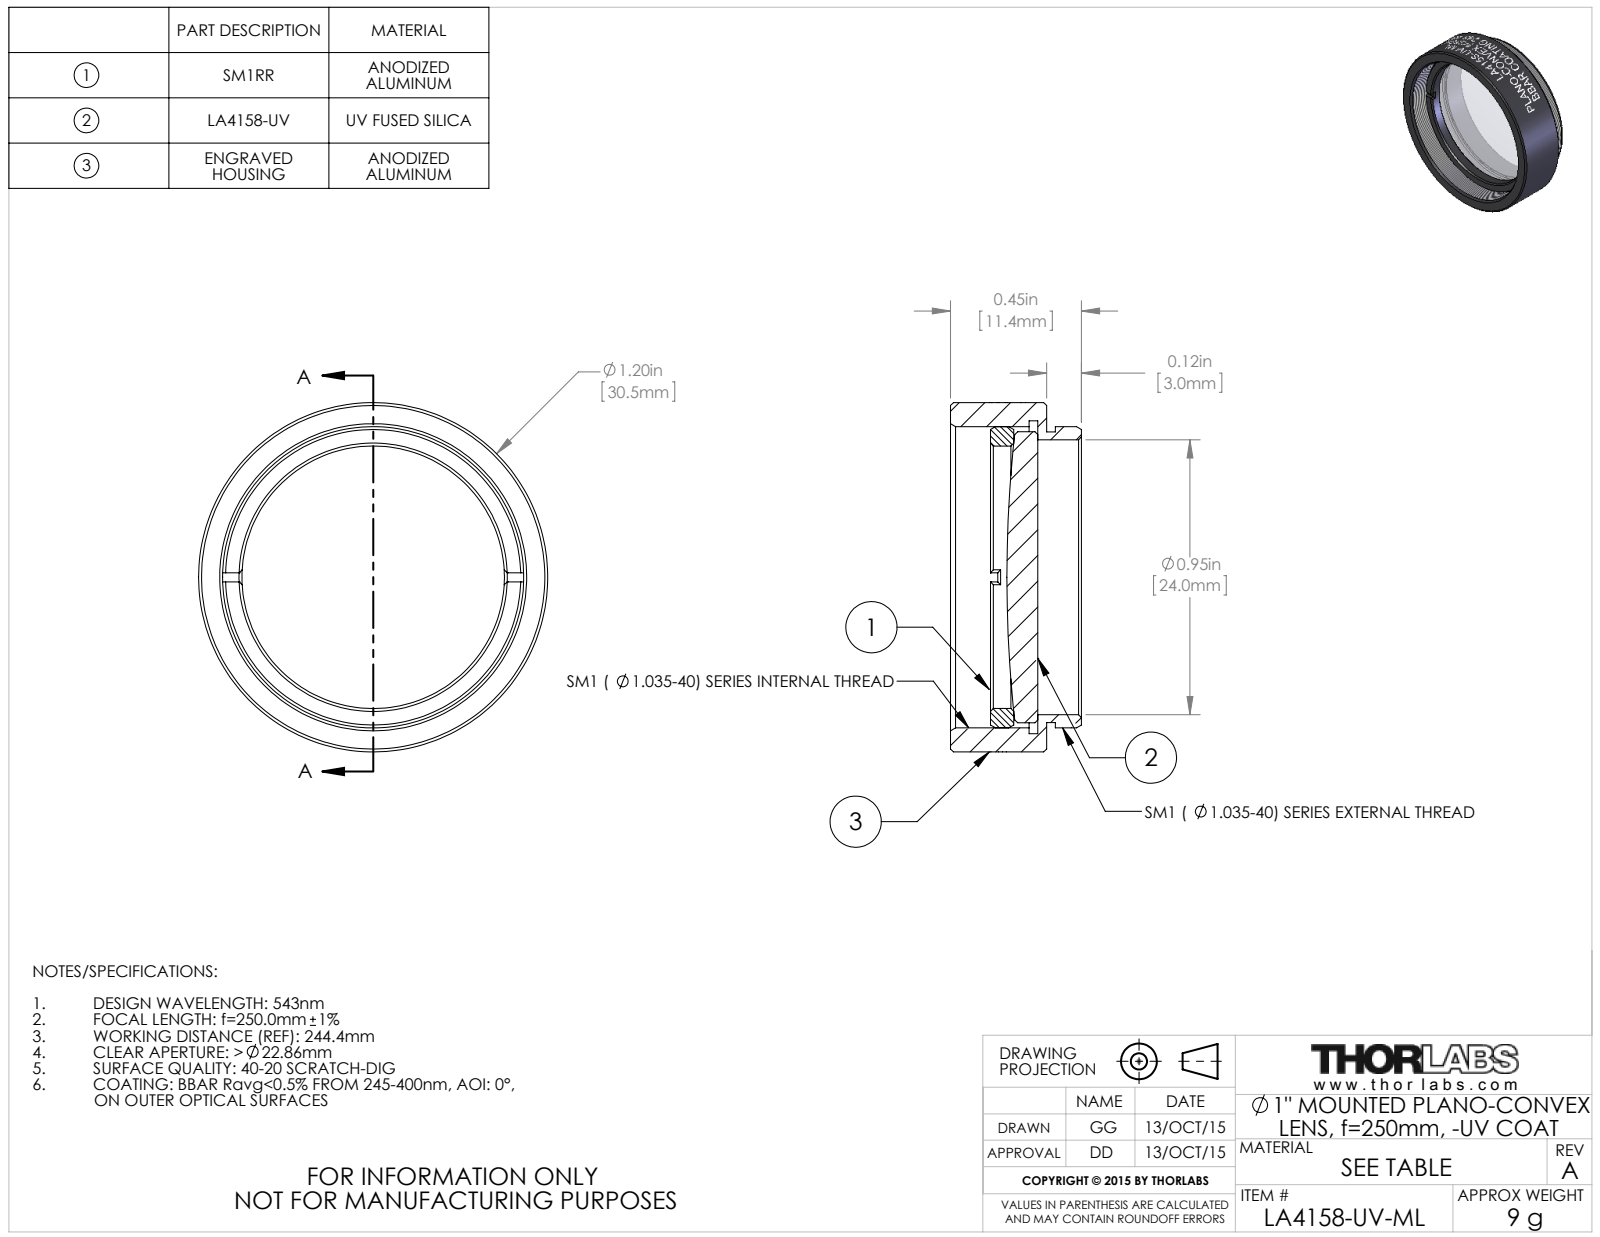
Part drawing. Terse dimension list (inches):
name: TTN039189-E0W
written by: SolidWorks 2014 (CONFIG_CONTROL_DESIGN)
unit: in
bodies: 3 solids, 161 faces (20 planar, 113 cylindrical, 28 other)
size: 1.2 × 1.2 × 0.45
volume: 0.199 in³; area: 6.653 in²
holes: 1× ⌀0.902, 1× ⌀0.945, 1× ⌀1.075
bosses: 1× ⌀1.2, 1× ⌀1.035, 1× ⌀1, 1× ⌀0.999
face distances: 0.03, 0.33, 0.3, 0.113, 0.083, 0.217, 0.193, 0.163, 0.08, 0.137
